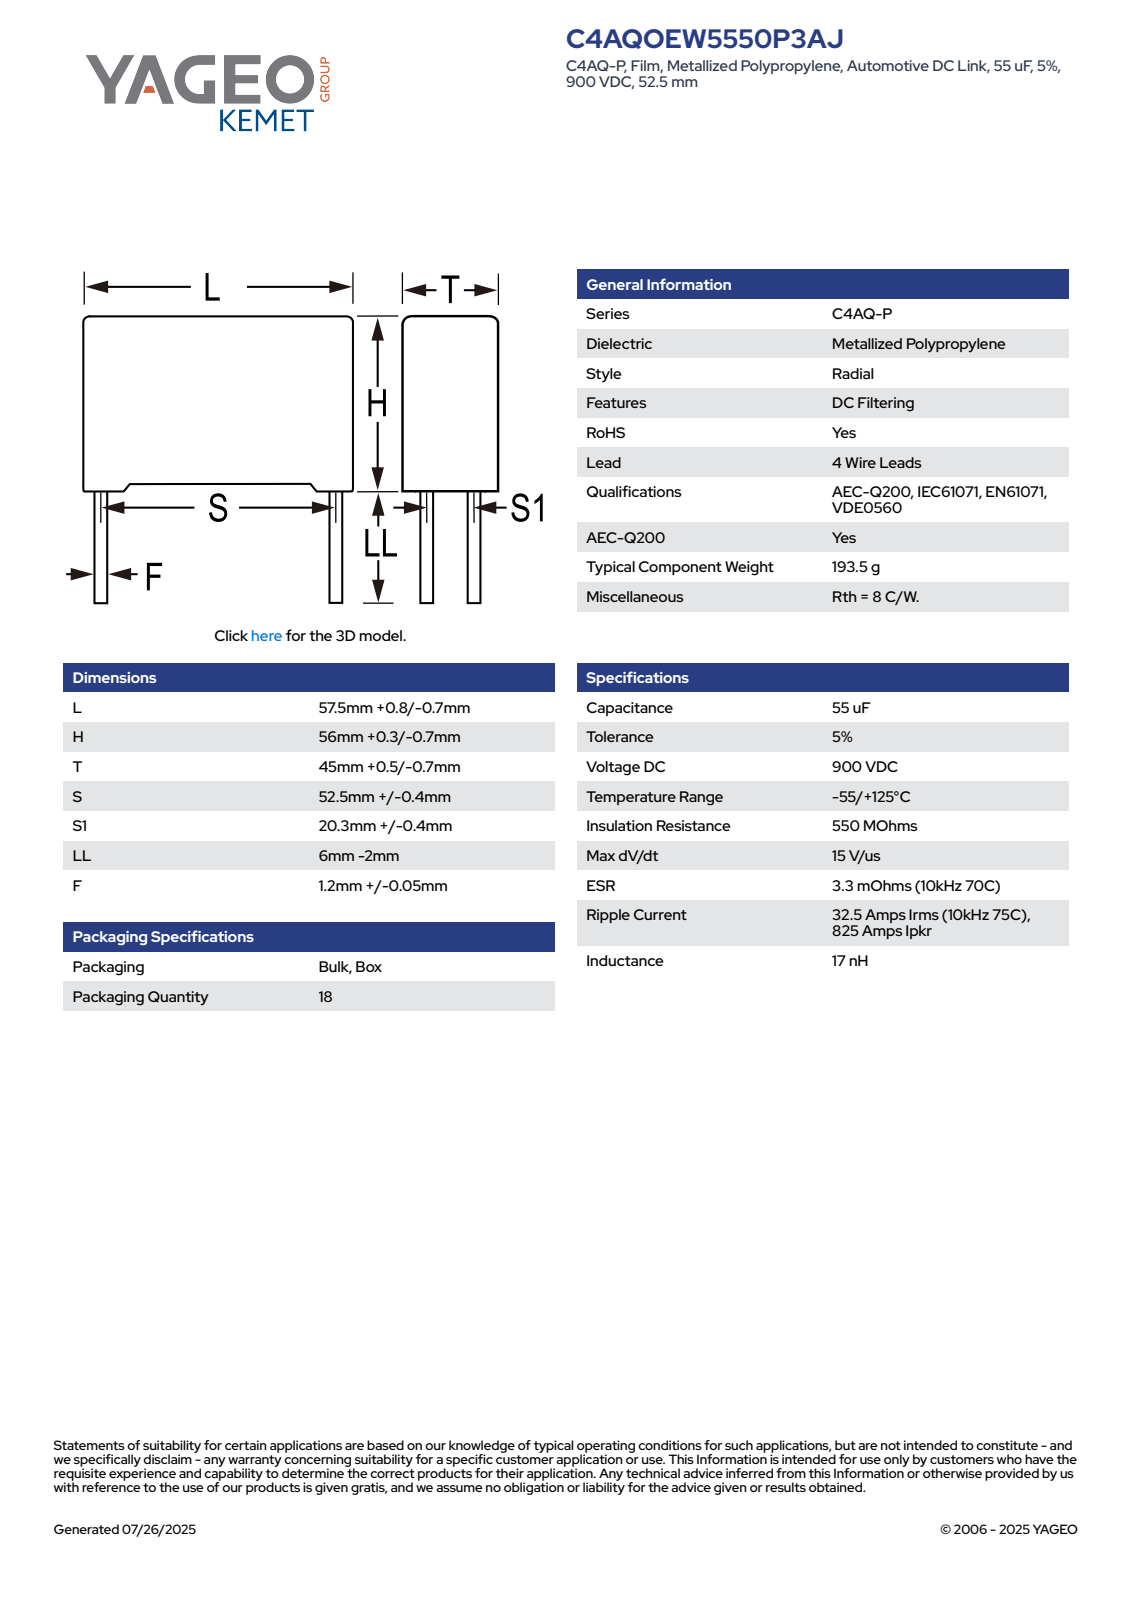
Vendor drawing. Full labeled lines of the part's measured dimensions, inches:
Part name (STEP PRODUCT): CFP_RB4_57.5X56X45_L58.3H56.3T45.5S52.5S120.3LL4F1.25
STEP written by: SolidWorks 2014 (AUTOMOTIVE_DESIGN)
Units: inches
Bodies: 4 solids, 91 faces (83 planar, 8 cylindrical, 0 other)
Overall size (bounding box): 2.374 × 2.295 × 1.792
Volume: 8.878 in³ · Surface area: 26.84 in²
Round bosses / shafts (diameter × count): ⌀0.049 ×4
Main face-to-face distances: 1.791, 2.295, 2.151, 0.065, 2.217, 0.11, 2.185, 2.075, 1.681, 1.571
